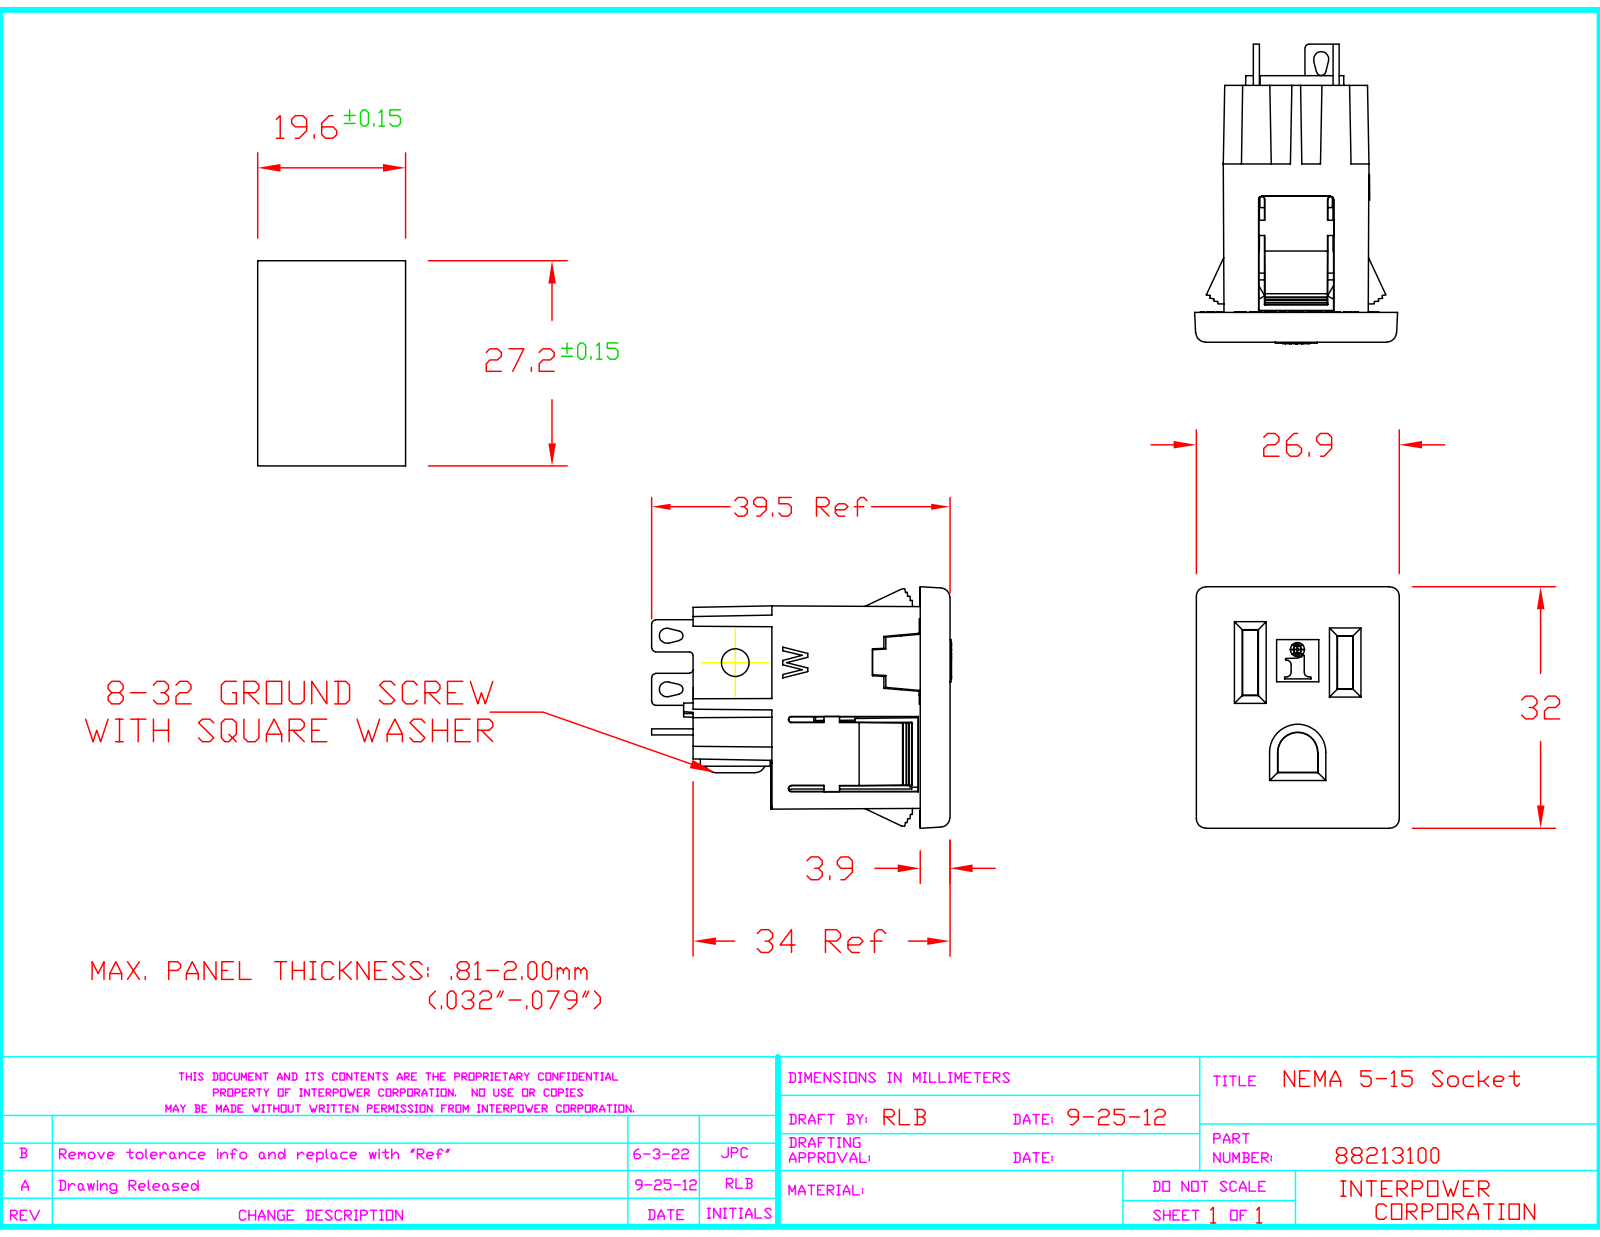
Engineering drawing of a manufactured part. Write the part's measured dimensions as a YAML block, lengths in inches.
part_name: "55030610-R2_NEMA_Contact_Solder-Tab.2; 55030610-R2_NEMA_Contact_Solder-Tab_Assy; 55030780-R4_NEMA-GROUND-SO_11-9-11; Contacts_Solder-Tab_Assy (+6 more)"
step_written_by: "OneSpace Designer 14.50 18-Oct-2006 (C) CoCreate Software GmbH (AUTOMOTIVE_DESIGN)"
units: inches
bodies: {solids: 7, faces: 2565, planar: 2294, cylindrical: 239, other: 32}
overall_size: [1.567, 1.259, 1.059]
volume: 0.569
surface_area: 20.86
round_holes:
  - {diameter: 0.146, count: 2}
  - {diameter: 0.173, count: 1}
round_bosses_or_shafts:
  - {diameter: 0.19, count: 2}
  - {diameter: 0.322, count: 1}
  - {diameter: 0.164, count: 1}
partial_cylinders:
  - {radius: 0.02, count: 45}
  - {radius: 0.015, count: 14}
  - {radius: 0.02, count: 11}
  - {radius: 0.03, count: 8}
  - {radius: 0.035, count: 8}
  - {radius: 0.05, count: 8}
  - {radius: 0.015, count: 7}
  - {radius: 0.052, count: 7}
face_to_face_distances: [0.031, 0.69, 0.08, 0.416, 0.85, 0.775, 0.155, 0.99, 0.99, 0.93]
